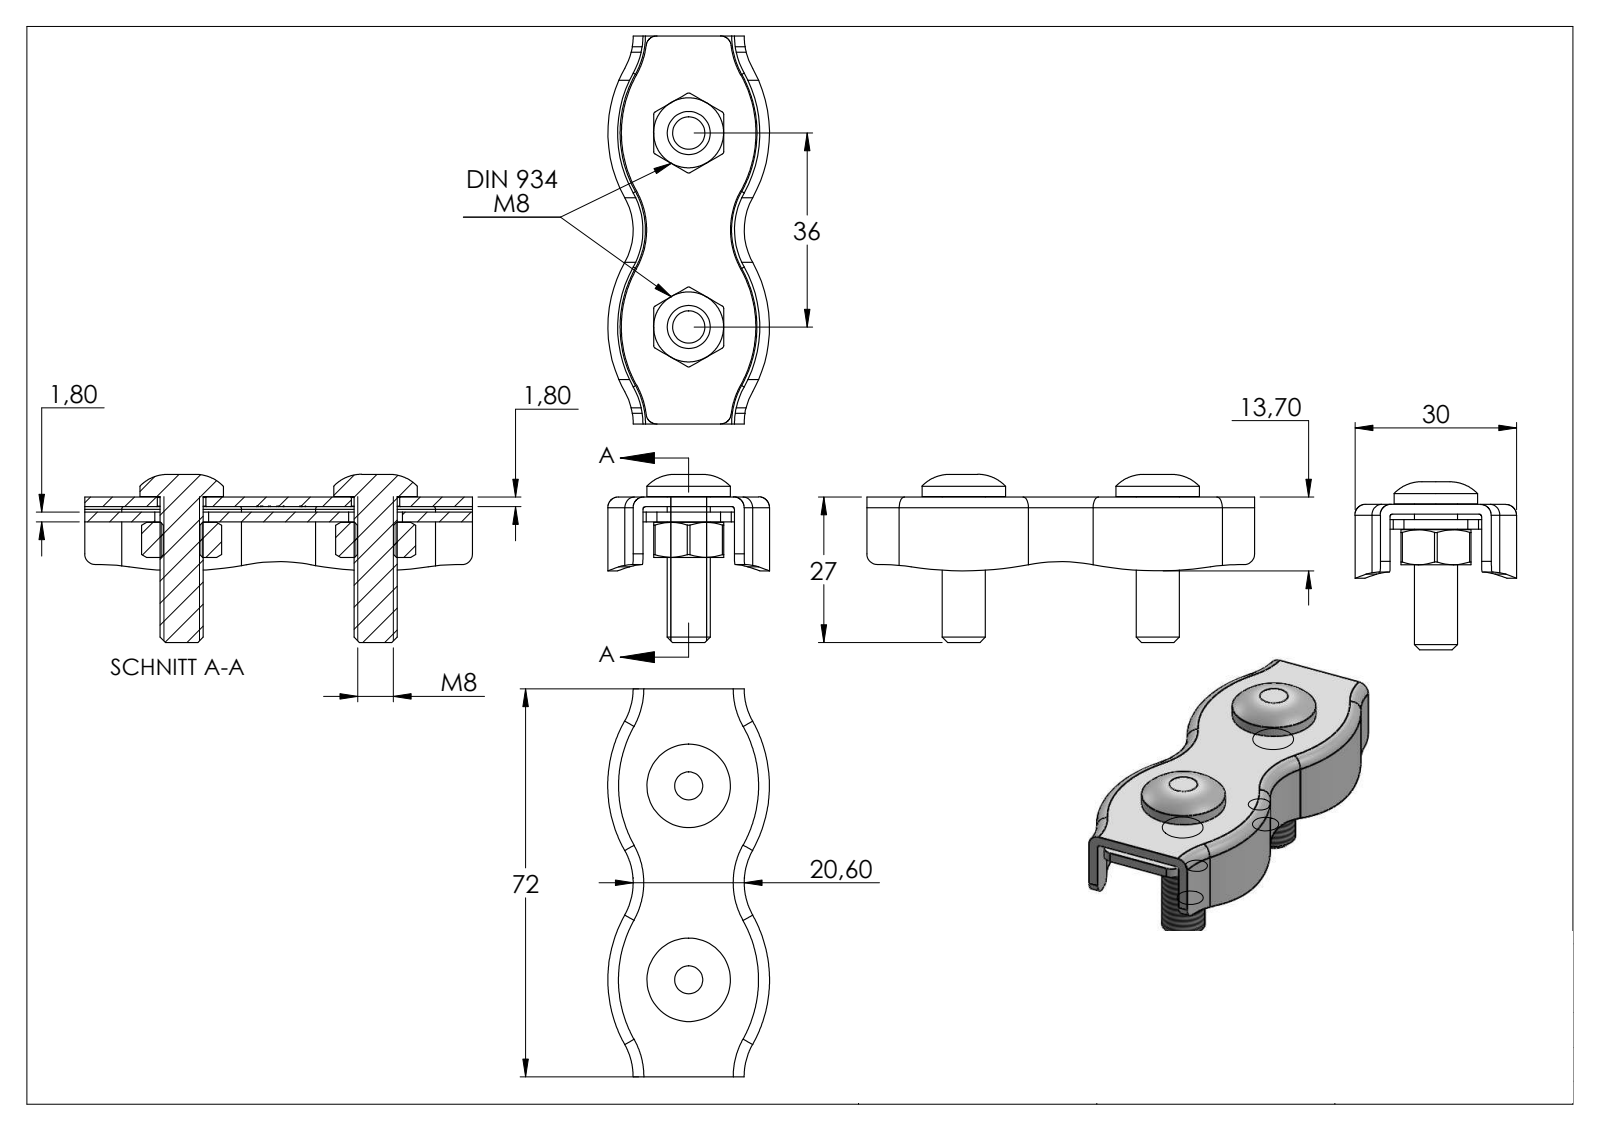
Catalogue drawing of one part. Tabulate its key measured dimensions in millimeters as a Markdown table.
| quantity | value |
| --- | --- |
| part name | 10006300X Teil2; 10006300X Teil1; 100063008; DIN 934 M4-M20_58321-240-8 (+3 more) |
| STEP written by | SolidWorks 2018 (CONFIG_CONTROL_DESIGN) |
| units | millimeters |
| bodies | 6 solids, 454 faces (149 planar, 80 cylindrical, 225 other) |
| overall size | 22000 × 3300 × 3300 |
| volume | 13 783 mm³ |
| surface area | 13 850 mm² |
| round holes (diameter × count) | 6.8 × 2, 9 × 2, 10 × 2 |
| round bosses / shafts (diameter × count) | 15.5 × 2, 8 × 2 |
| partial cylindrical surfaces (radius × count) | 0.5 × 12, 2 × 6, 12.27 × 6, 14.07 × 6, 14.77 × 6, 22.05 × 4, 22.75 × 4, 24.55 × 4 |
| main face-to-face distances | 1.8, 2.8, 1, 4.6, 2.9, 1.9, 4.7, 13, 31.18, 4.8 |
| hole center spacings | 36 |
